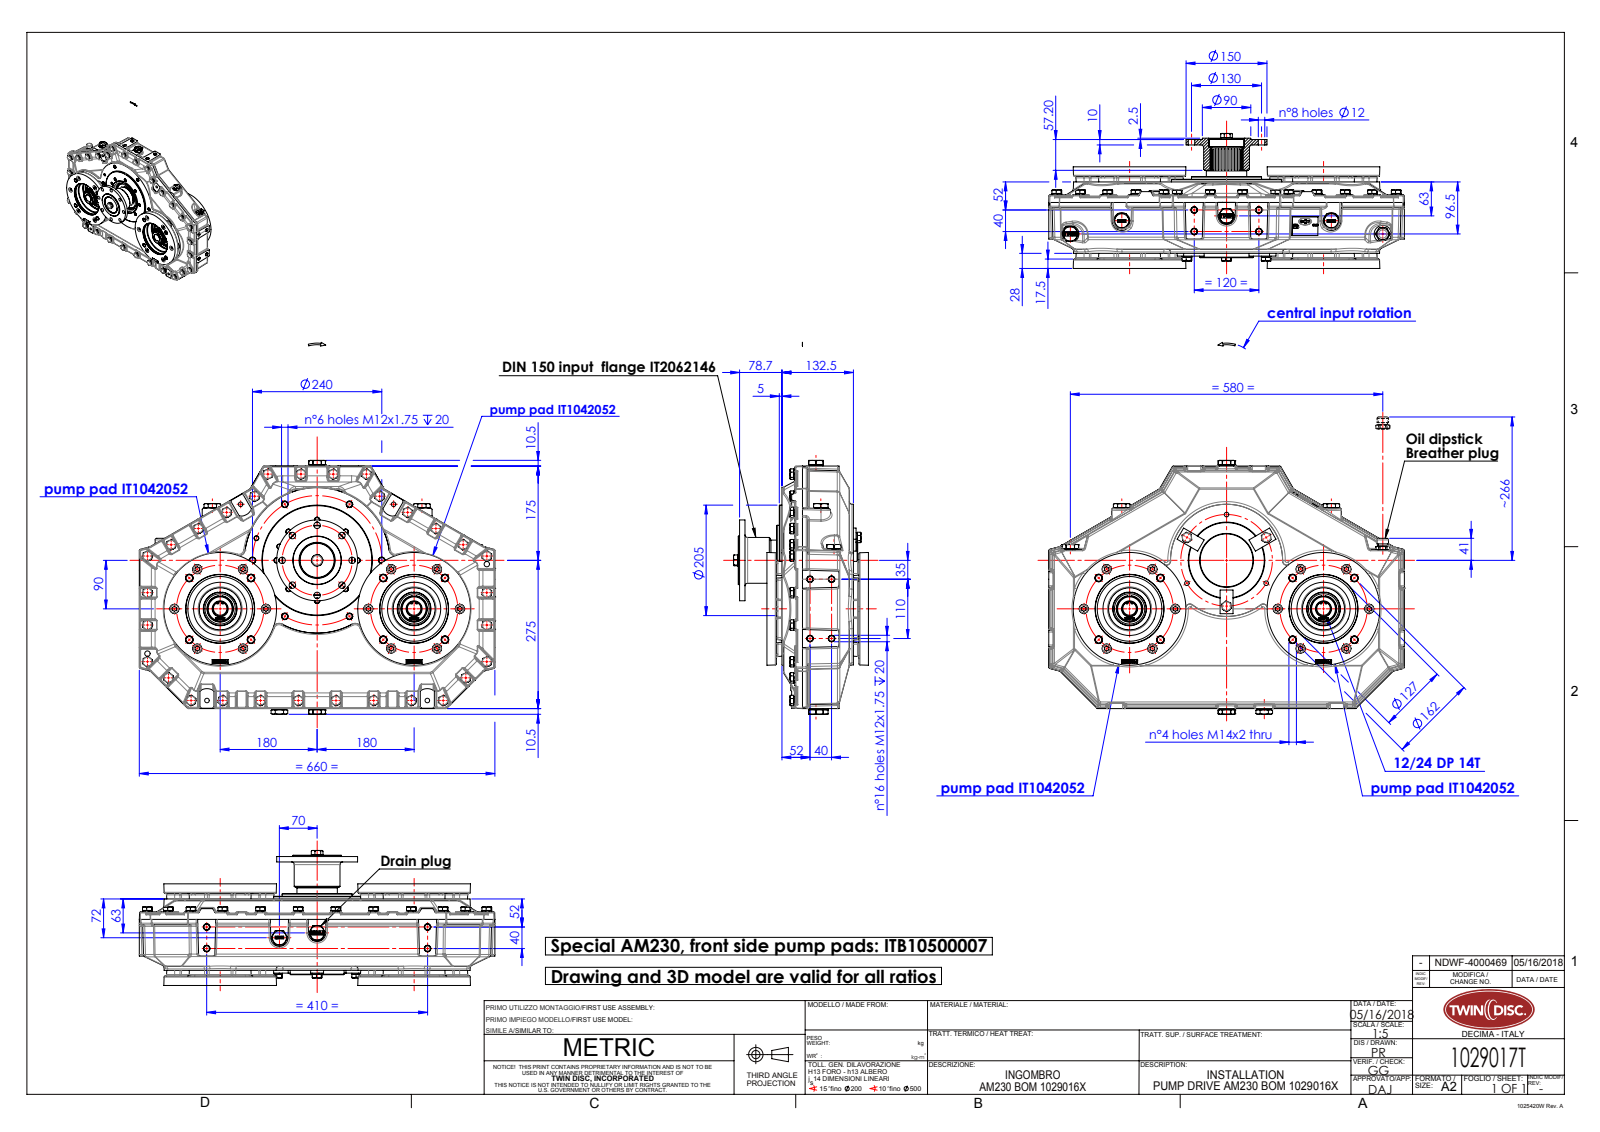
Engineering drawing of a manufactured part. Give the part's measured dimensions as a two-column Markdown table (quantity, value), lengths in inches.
| quantity | value |
| --- | --- |
| part name | IT1054022_rev00-installation; IT0000198_rev00-installation; ITam230-001_rev01-installation; ITam230-002_rev00-installation (+6 more) |
| STEP written by | SolidWorks 2015 (AUTOMOTIVE_DESIGN) |
| units | inches |
| bodies | 65 solids, 7947 faces (3689 planar, 1924 cylindrical, 2334 other) |
| overall size | 27.167 × 25.984 × 9.862 |
| volume | 295.1 in³ |
| surface area | 3 571 in² |
| round holes (diameter × count) | 0.402 × 51, 0.472 × 34, 0.335 × 30, 0.413 × 30, 0.433 × 15, 0.669 × 12, 0.394 × 10, 0.551 × 8, 0.079 × 4, 0.728 × 3, 0.827 × 3, 3.15 × 3 |
| round bosses / shafts (diameter × count) | 0.394 × 45, 0.638 × 33, 0.713 × 32, 0.63 × 12, 3.886 × 3, 3.228 × 3, 1.063 × 3, 1.022 × 3 |
| partial cylindrical surfaces (radius × count) | 0.079 × 201, 0.118 × 151, 0.098 × 78, 0.197 × 74, 0.018 × 58, 0.512 × 19, 0.059 × 14, 0.073 × 4 |
| main face-to-face distances | 1.102, 5.217, 6.319, 4.921, 1.22, 4.803, 7.421, 0.413, 6.732, 0.689 |
| hole center spacings | 4.724, 2.26, 2.953, 5.456, 1.575, 8.183, 0.889, 2.022 |
